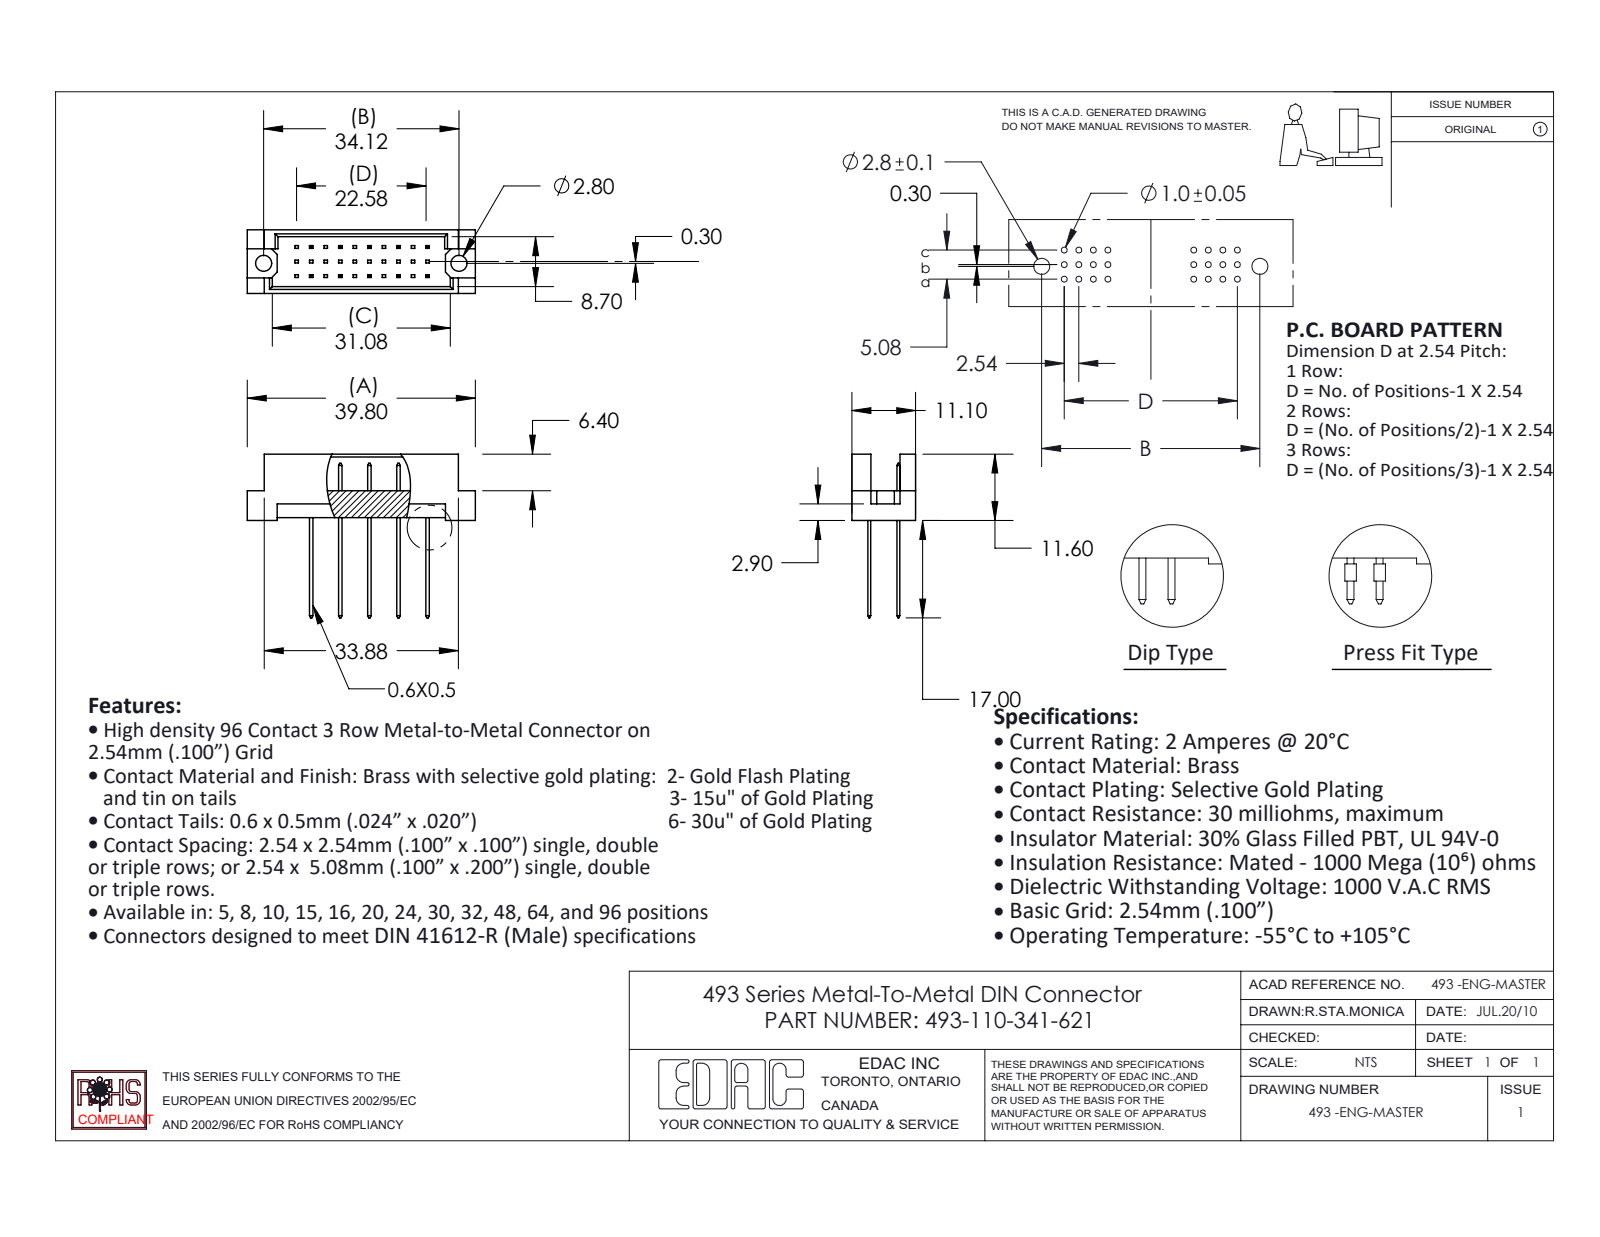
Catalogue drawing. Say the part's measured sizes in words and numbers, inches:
The part is named "493 Part_30; 493-290_41; 493-110-341-621". Its 3-D file was written by "SolidWorks 2020 (CONFIG_CONTROL_DESIGN)". It is 11 solids with 312 faces: 308 planar, 4 cylindrical and 0 other. Overall it measures 1.567 by 1.126 by 0.437 inches. Its volume is 0.15 cubic inches and its surface area 5.158 square inches. Round holes: 2 of diameter 0.11. The main face-to-face distances are 0.2, 0.047, 0.39, 0.437, 0.02, 0.343, 0.185, 0.109, 0.128, 0.309. The hole center spacings are 1.343.
